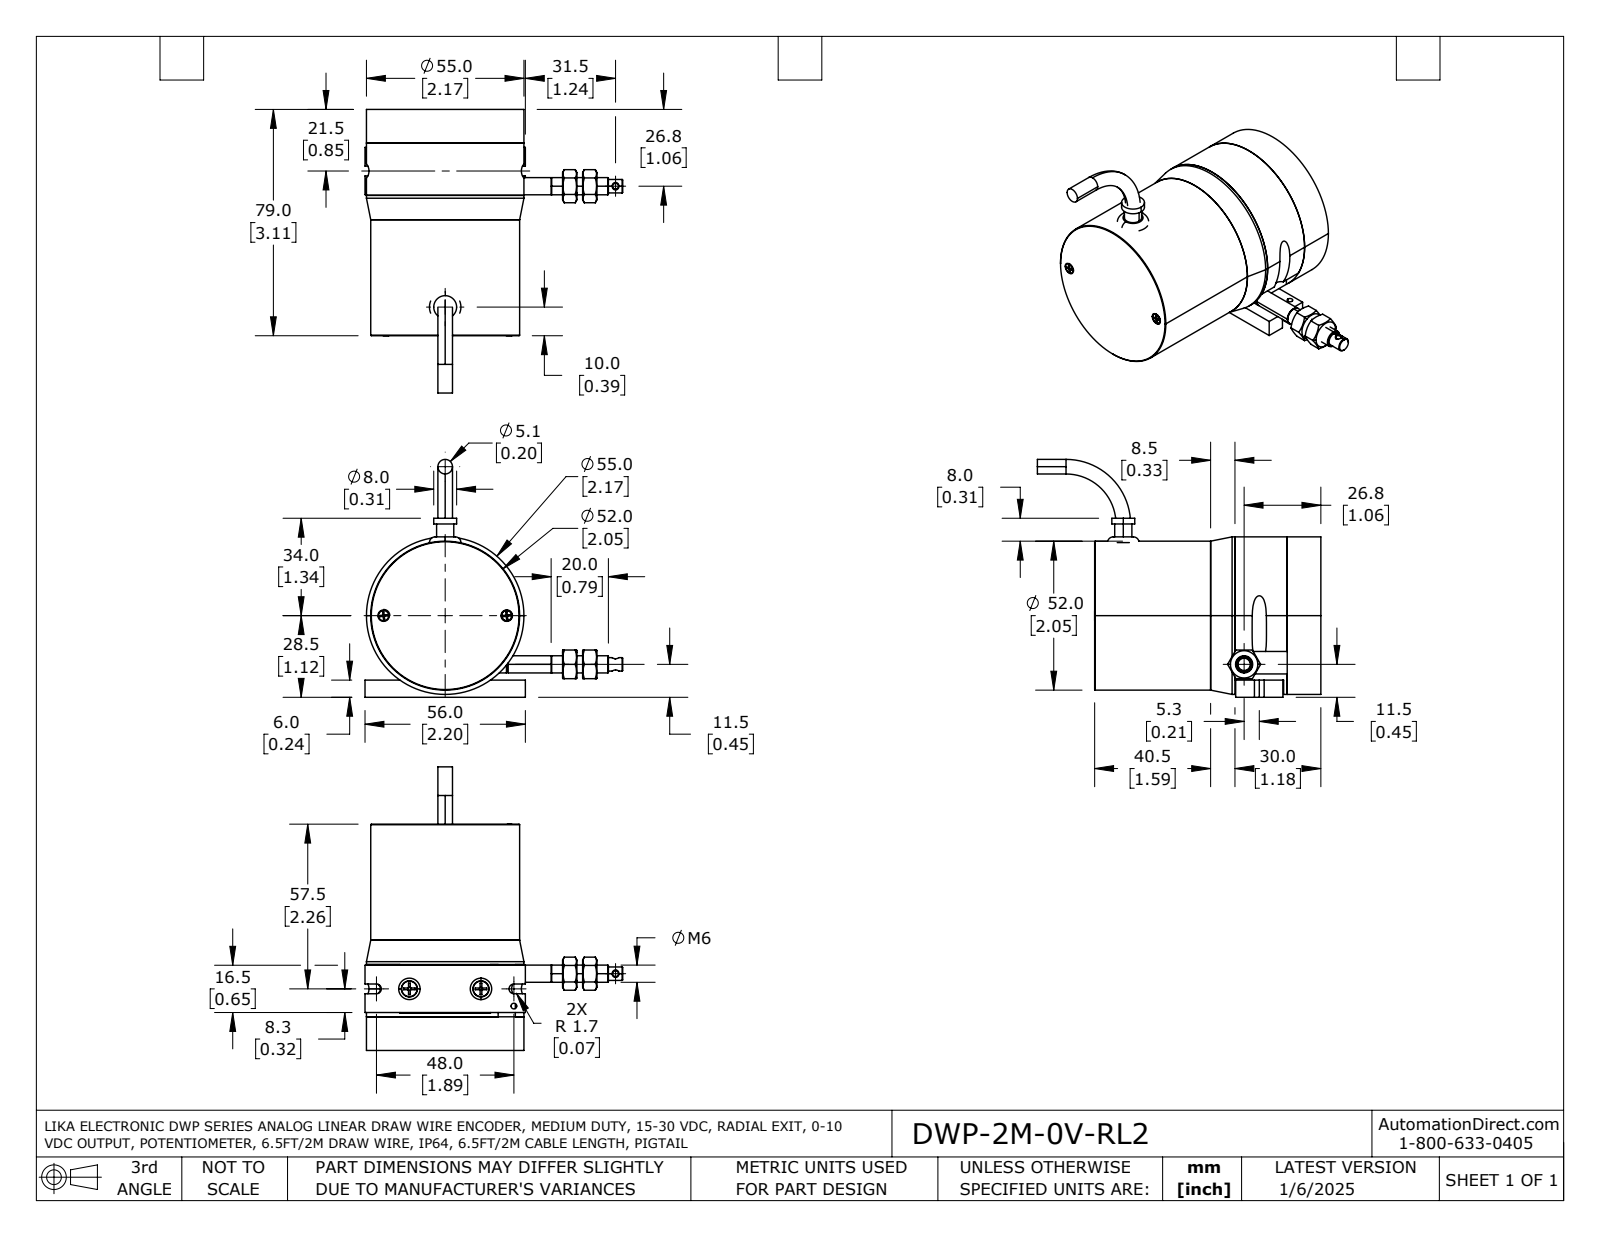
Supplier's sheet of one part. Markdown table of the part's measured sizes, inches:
| quantity | value |
| --- | --- |
| part name | DWP-2M-0V-RL2 |
| STEP written by | SolidWorks 2021 (AUTOMOTIVE_DESIGN) |
| units | inches |
| bodies | 20 solids, 588 faces (164 planar, 216 cylindrical, 208 other) |
| overall size | 3.898 × 3.543 × 3.27 |
| volume | 4.345 in³ |
| surface area | 73.56 in² |
| round holes (diameter × count) | 0.063 × 8, 0.197 × 7, 0.079 × 5, 0.081 × 4, 0.083 × 4, 0.11 × 4, 0.059 × 2, 0.087 × 2, 0.098 × 2, 0.134 × 2, 0.031 × 1, 0.157 × 1 |
| round bosses / shafts (diameter × count) | 0.118 × 3, 0.236 × 2, 0.201 × 2, 0.098 × 2, 0.079 × 2, 2.165 × 1, 2.047 × 1, 1.874 × 1 |
| partial cylindrical surfaces (radius × count) | 0.007 × 18, 0.008 × 6, 0.315 × 5, 0.098 × 3, 0.067 × 2, 0.197 × 1, 0.787 × 1, 1.053 × 1 |
| main face-to-face distances | 0.079, 3.031, 1.181, 3.11, 1.929, 1.85, 0.384, 0.463, 0.719, 2.569 |
| hole center spacings | 0.196, 0.669, 0.846, 0.946, 1.079, 1.158, 0.098, 0.177 |
